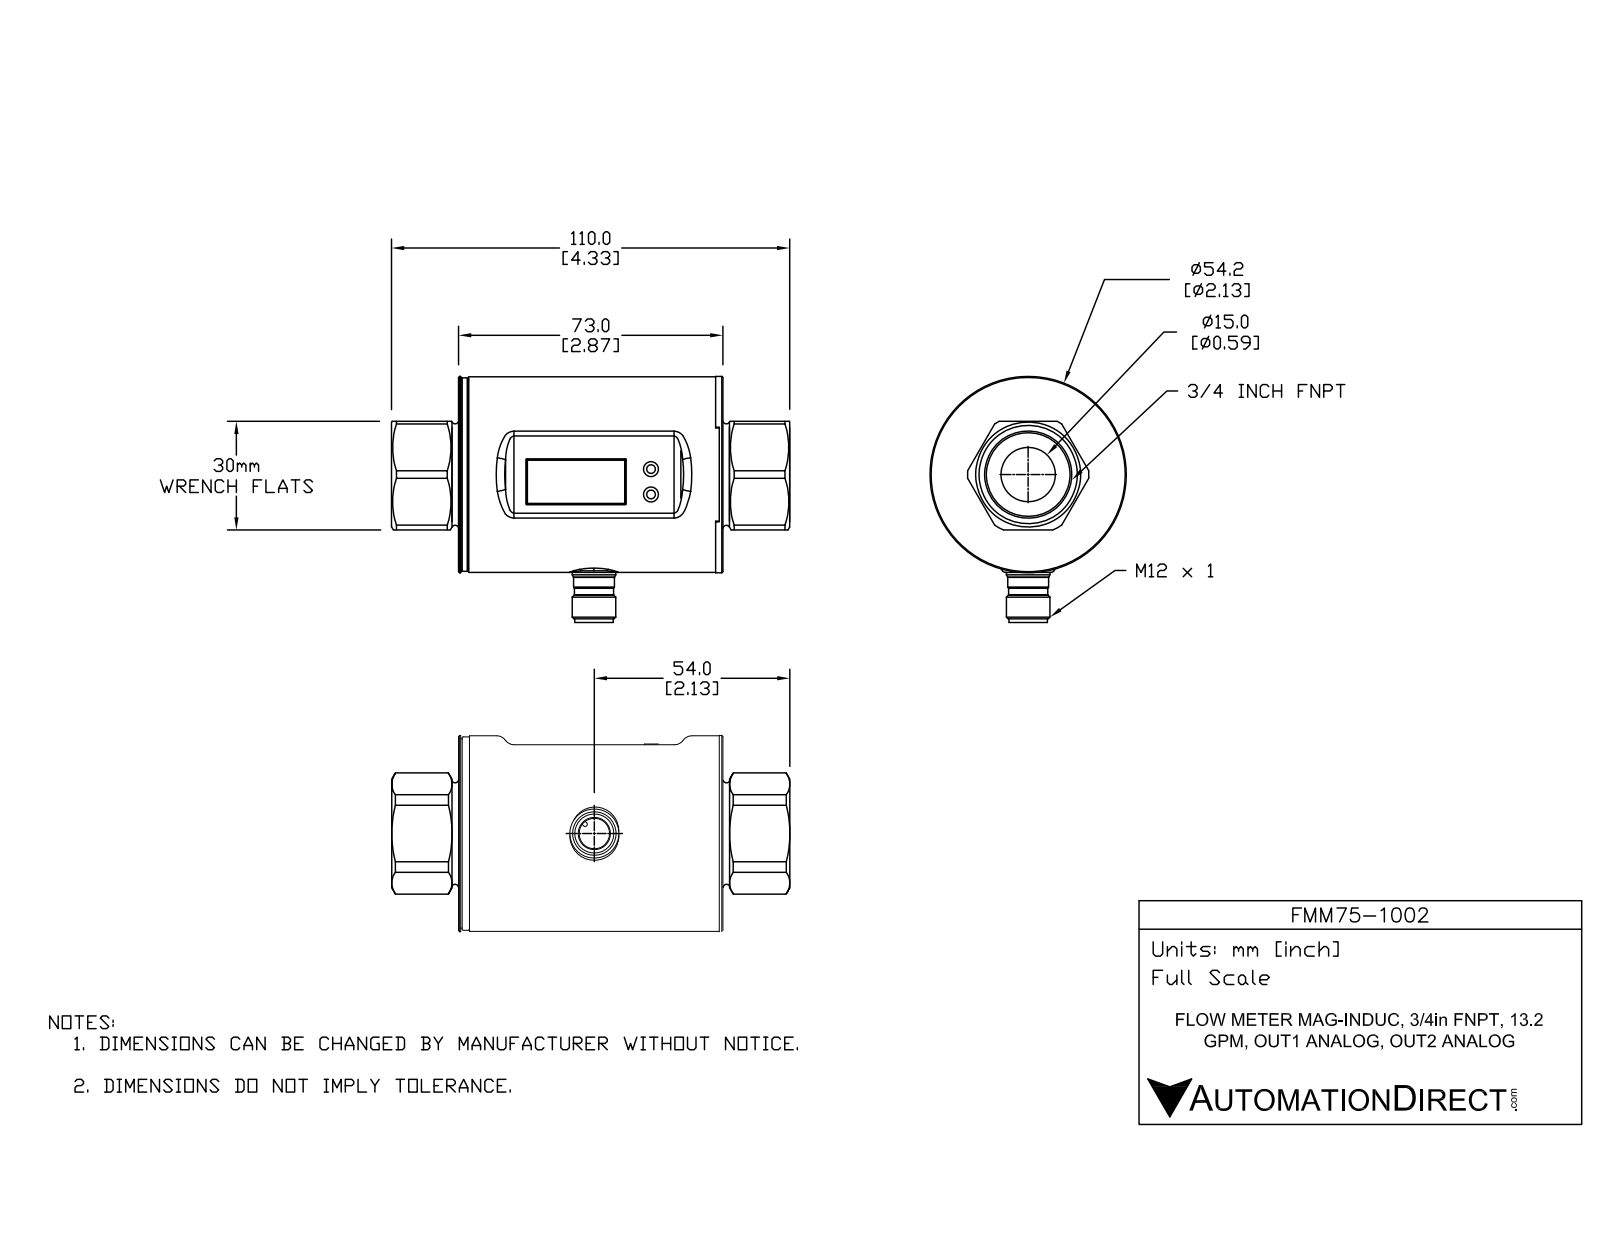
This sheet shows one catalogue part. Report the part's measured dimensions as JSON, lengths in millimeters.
{"part_name": "FMM75-1002", "step_written_by": "SolidWorks 2015 (AUTOMOTIVE_DESIGN)", "units": "millimeters", "bodies": {"solids": 9, "faces": 204, "planar": 82, "cylindrical": 81, "other": 41}, "overall_size": [109.99, 67.85, 54.2], "volume_mm3": 47414, "surface_area_mm2": 55956, "round_holes": [[1.5, 2], [3.6, 2], [4.11, 2], [8.4, 1], [12, 1], [15, 1], [23.1, 1], [52, 1]], "round_bosses_or_shafts": [[3.9, 2], [54.2, 1], [54, 1], [53.4, 1], [52.2, 1], [12, 1], [11.3, 1], [10.6, 1]], "partial_cylinders_radius": [[1, 4], [0.3, 2], [2, 2], [3, 2], [0.6, 1], [16.75, 1]], "face_to_face_distances": [70, 2, 5, 68, 71.7, 1, 72, 72.7, 73, 3], "hole_center_spacings": [13, 1.25, 7, 8, 9.25, 21, 22.25, 26]}
